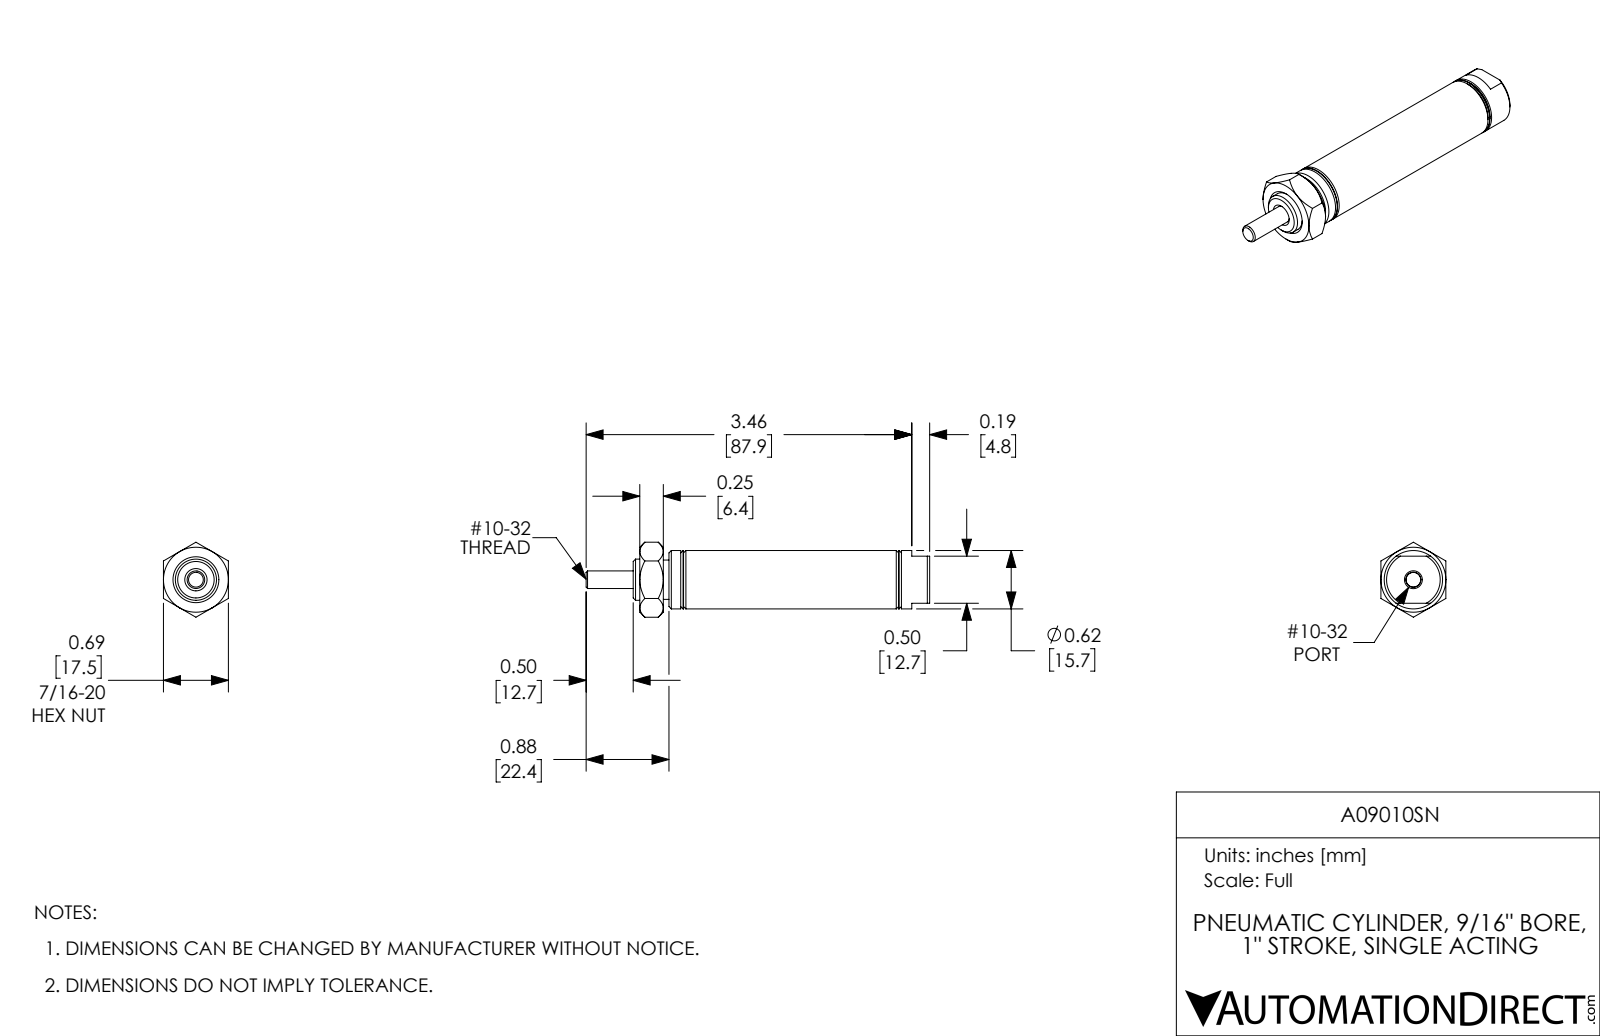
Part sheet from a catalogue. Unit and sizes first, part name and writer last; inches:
Units: inches
Overall size (bounding box): 3.65 × 0.797 × 0.69
Round holes (diameter × count): ⌀0.156 ×1, ⌀0.159 ×1, ⌀0.187 ×1, ⌀0.19 ×1, ⌀0.437 ×1, ⌀0.563 ×1
Round bosses / shafts (diameter × count): ⌀0.62 ×1, ⌀0.417 ×1
Main face-to-face distances: 0.635, 2.135, 0.5, 0.69, 0.945, 1.945, 1.5, 2.83, 2.195, 0.695
Volume: 0.725 in³ · Surface area: 14.89 in²
Bodies: 3 solids, 95 faces (27 planar, 30 cylindrical, 38 other)
Part name (STEP PRODUCT): A09010SN-MainBody; A09010SN; A09010SN-Rod; A09010SN_Mounting Nut_D-154
STEP written by: SolidWorks 2017 (AUTOMOTIVE_DESIGN)
